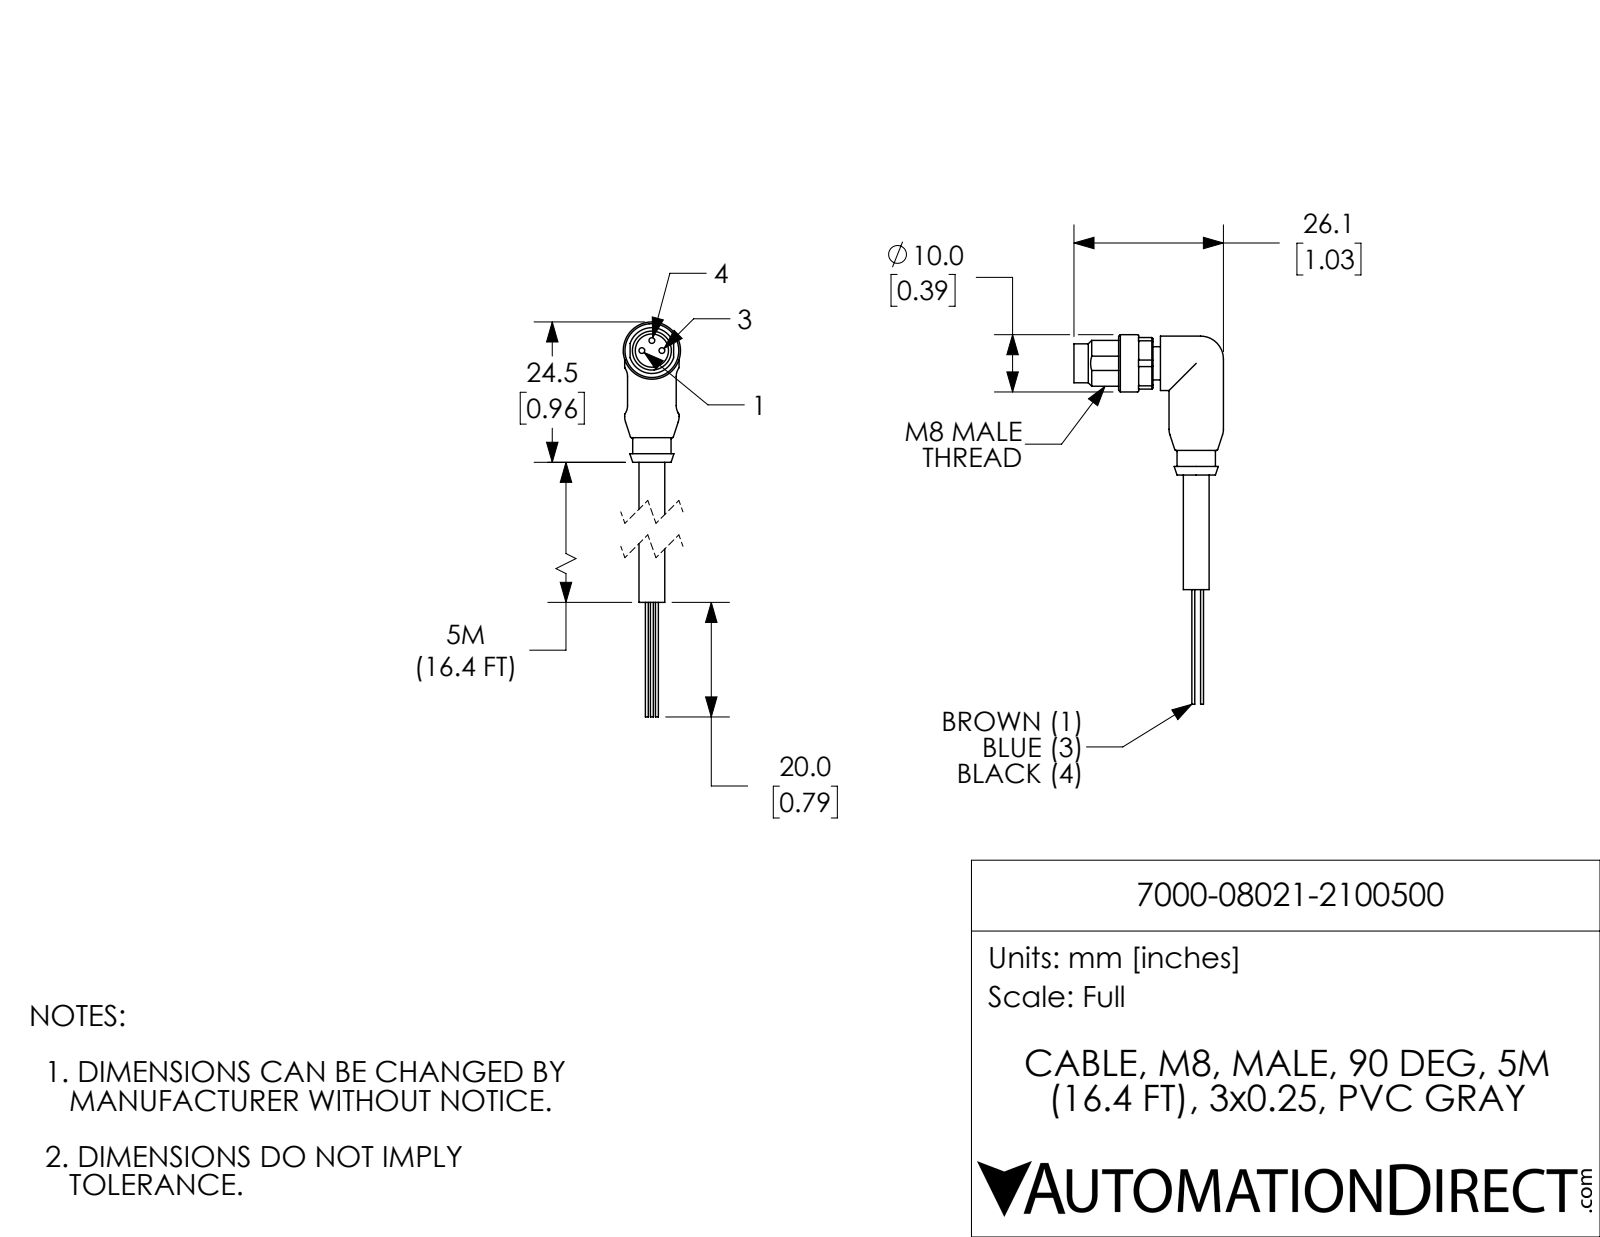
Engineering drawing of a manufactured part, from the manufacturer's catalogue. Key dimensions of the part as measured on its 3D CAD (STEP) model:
Part name (STEP PRODUCT): 7000-08021-2100500
STEP written by: SolidWorks 2017 (AUTOMOTIVE_DESIGN)
Units: inches
Bodies: 4 solids, 118 faces (40 planar, 45 cylindrical, 33 other)
Overall size (bounding box): 2.539 × 1.028 × 0.394
Volume: 0.161 in³ · Surface area: 2.831 in²
Round holes (diameter × count): ⌀0.228 ×1
Round bosses / shafts (diameter × count): ⌀0.039 ×3, ⌀0.02 ×3, ⌀0.374 ×2, ⌀0.394 ×1, ⌀0.315 ×1, ⌀0.268 ×1, ⌀0.264 ×1, ⌀0.177 ×1
Partial cylindrical surfaces — rounded edges, fillets, slot ends (radius × count): R0.008 ×4, R0.098 ×4, R0.193 ×1
Main face-to-face distances: 0.051, 0.354, 0.018, 0.317, 0.346, 0.398, 0.335, 0.11, 0.236, 0.287
